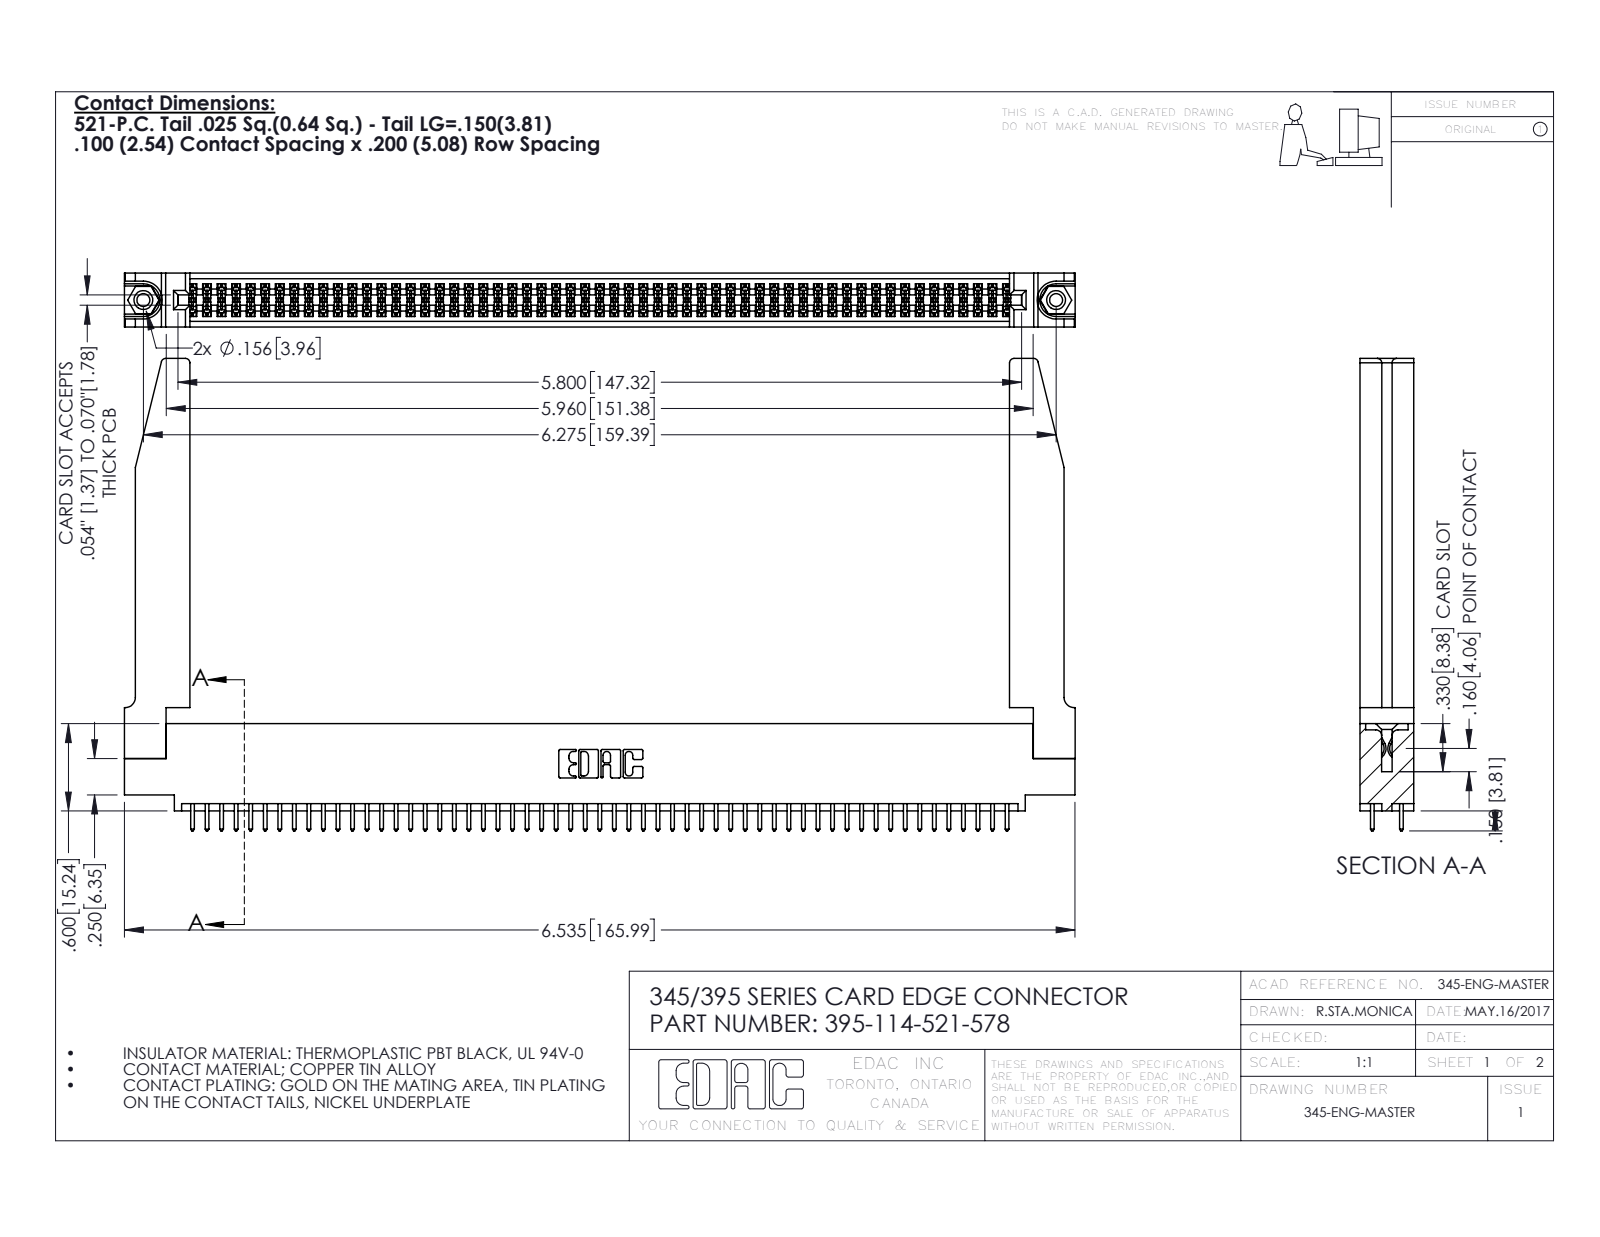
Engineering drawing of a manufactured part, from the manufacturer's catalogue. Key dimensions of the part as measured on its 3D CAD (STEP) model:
Part name (STEP PRODUCT): 345 Part_0.110 Offset - 0.156 Dia-TH; 345-250-001_345-250-001-102; 395-114-521-578; 345-292-001_345-293-121 (+1 more)
STEP written by: SolidWorks 2016 (CONFIG_CONTROL_DESIGN)
Units: inches
Bodies: 119 solids, 6064 faces (3988 planar, 2024 cylindrical, 52 other)
Overall size (bounding box): 6.536 × 3.247 × 0.37
Volume: 1.459 in³ · Surface area: 47.72 in²
Round holes (diameter × count): ⌀0.089 ×2, ⌀0.125 ×2, ⌀0.156 ×2, ⌀0.064 ×1
Round bosses / shafts (diameter × count): ⌀0.155 ×2
Partial cylindrical surfaces — rounded edges, fillets, slot ends (radius × count): R0.006 ×171, R0.01 ×114, R0.01 ×22, R0.03 ×8, R0.007 ×6, R0.031 ×6, R0.026 ×3, R0.014 ×2
Main face-to-face distances: 0.072, 0.298, 0.37, 0.2, 0.098, 0.272, 0.025, 0.225, 0.175, 0.148
Hole centre spacings: 0.27, 6.039, 6.275
